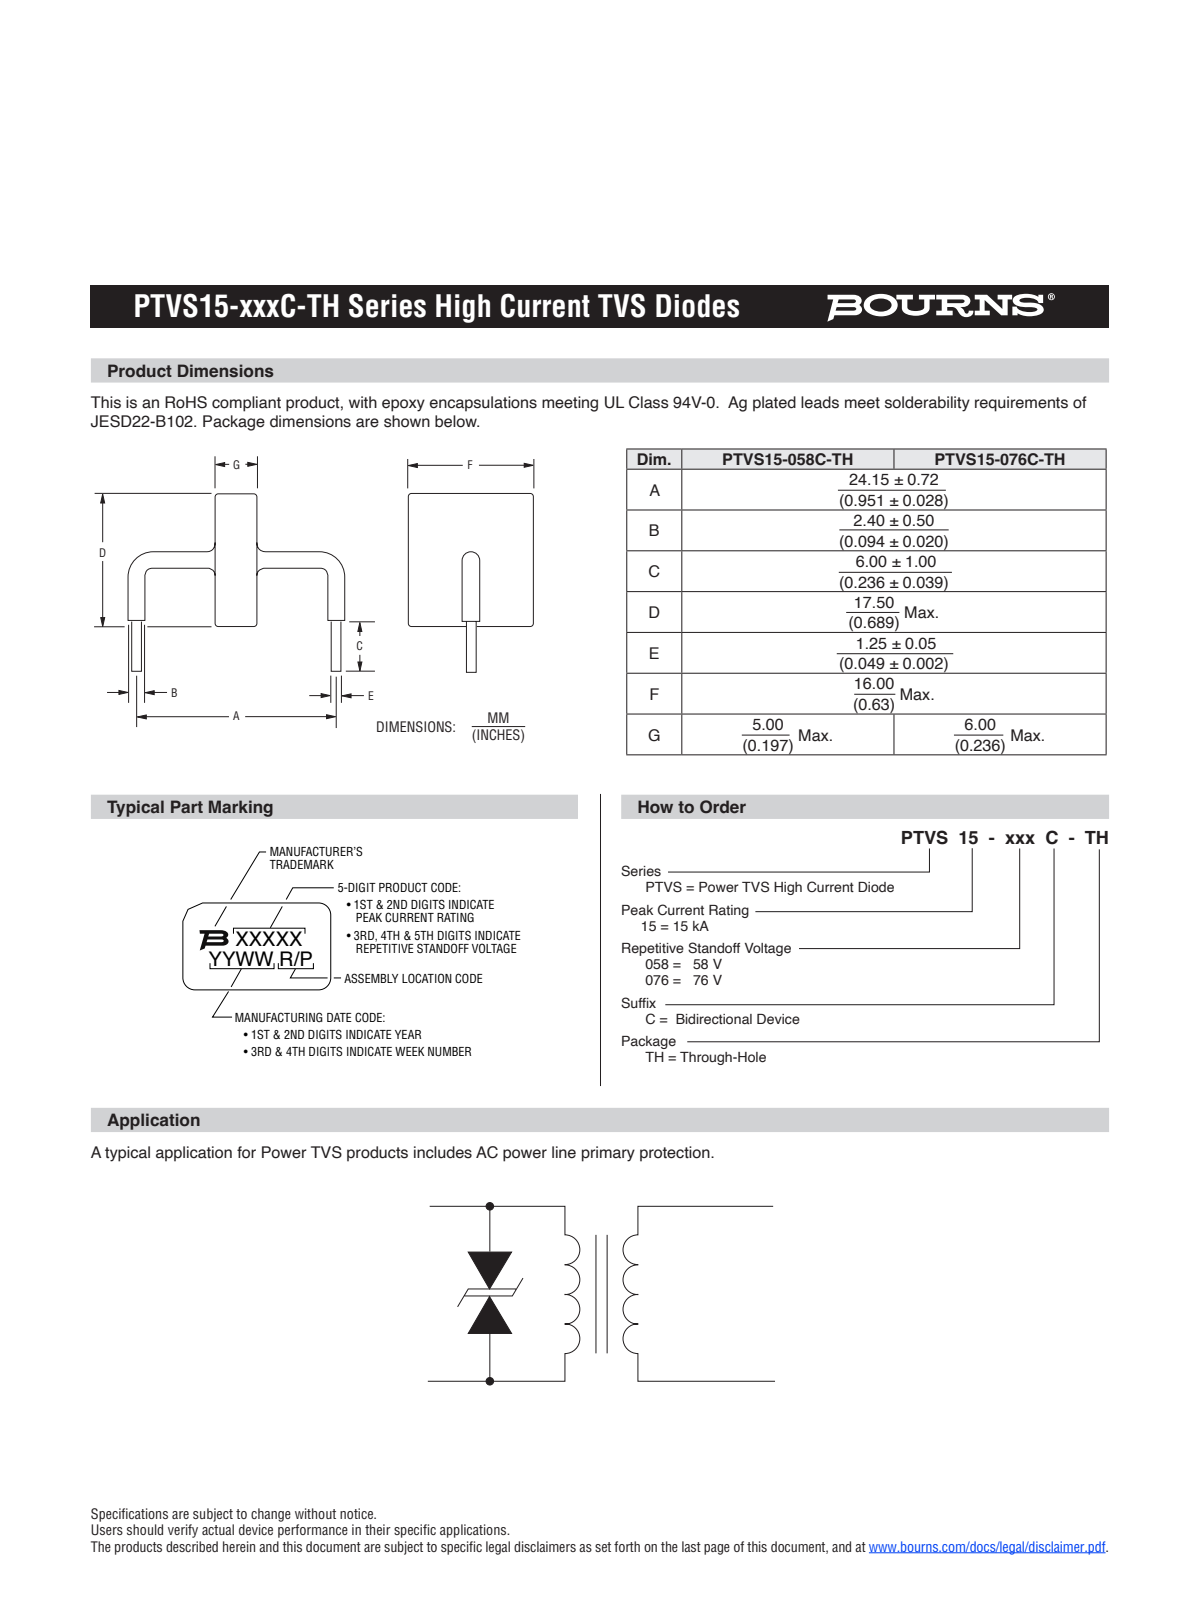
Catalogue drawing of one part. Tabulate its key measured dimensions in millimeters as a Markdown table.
| quantity | value |
| --- | --- |
| part name | PTVS15KA-xxC-TH |
| STEP written by | SolidWorks 2012 (CONFIG_CONTROL_DESIGN) |
| units | millimeters |
| bodies | 1 solid, 71 faces (14 planar, 32 cylindrical, 25 other) |
| overall size | 26.55 × 22 × 15.2 |
| volume | 1 340 mm³ |
| surface area | 1 012 mm² |
| round bosses / shafts (diameter × count) | 2.41 × 2, 2.4 × 2, 1.25 × 2 |
| partial cylindrical surfaces (radius × count) | 1 × 16, 11 × 4 |
| main face-to-face distances | 5, 15.2, 16, 7.25 |
